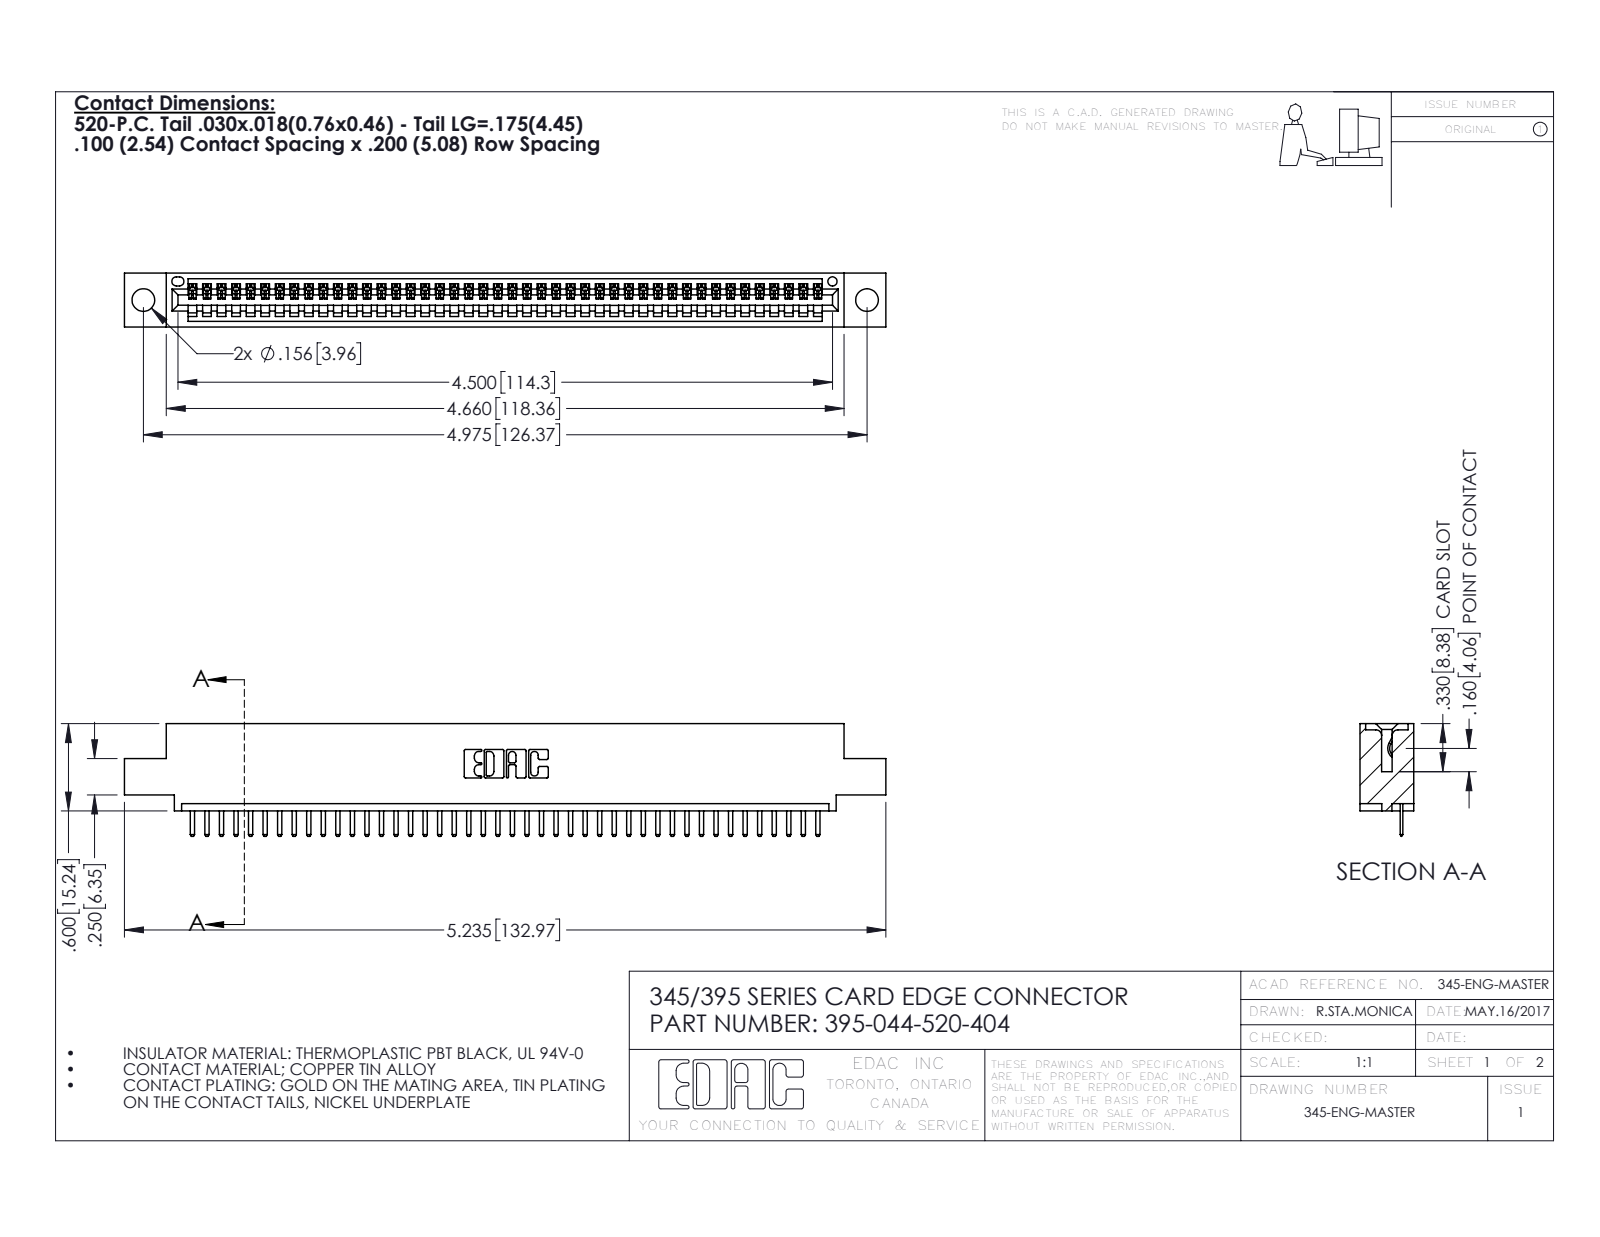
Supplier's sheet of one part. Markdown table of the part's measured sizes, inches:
| quantity | value |
| --- | --- |
| part name | 345 Part_0.110 Offset - 0.156 Dia-TH; 395-044-520-404; 345-292-001_345-293-120 |
| STEP written by | SolidWorks 2016 (CONFIG_CONTROL_DESIGN) |
| units | inches |
| bodies | 45 solids, 2858 faces (1932 planar, 926 cylindrical, 0 other) |
| overall size | 5.235 × 0.775 × 0.37 |
| volume | 0.754 in³ |
| surface area | 24.69 in² |
| round holes (diameter × count) | 0.156 × 2, 0.064 × 1 |
| partial cylindrical surfaces (radius × count) | 0.01 × 90, 0.006 × 88, 0.01 × 22, 0.007 × 6, 0.031 × 6, 0.026 × 3, 0.031 × 2, 0.04 × 2 |
| main face-to-face distances | 0.298, 0.072, 0.37, 0.2, 0.098, 0.272, 0.025, 0.225, 0.072, 0.149 |
| hole center spacings | 0.27, 4.739, 4.975 |
